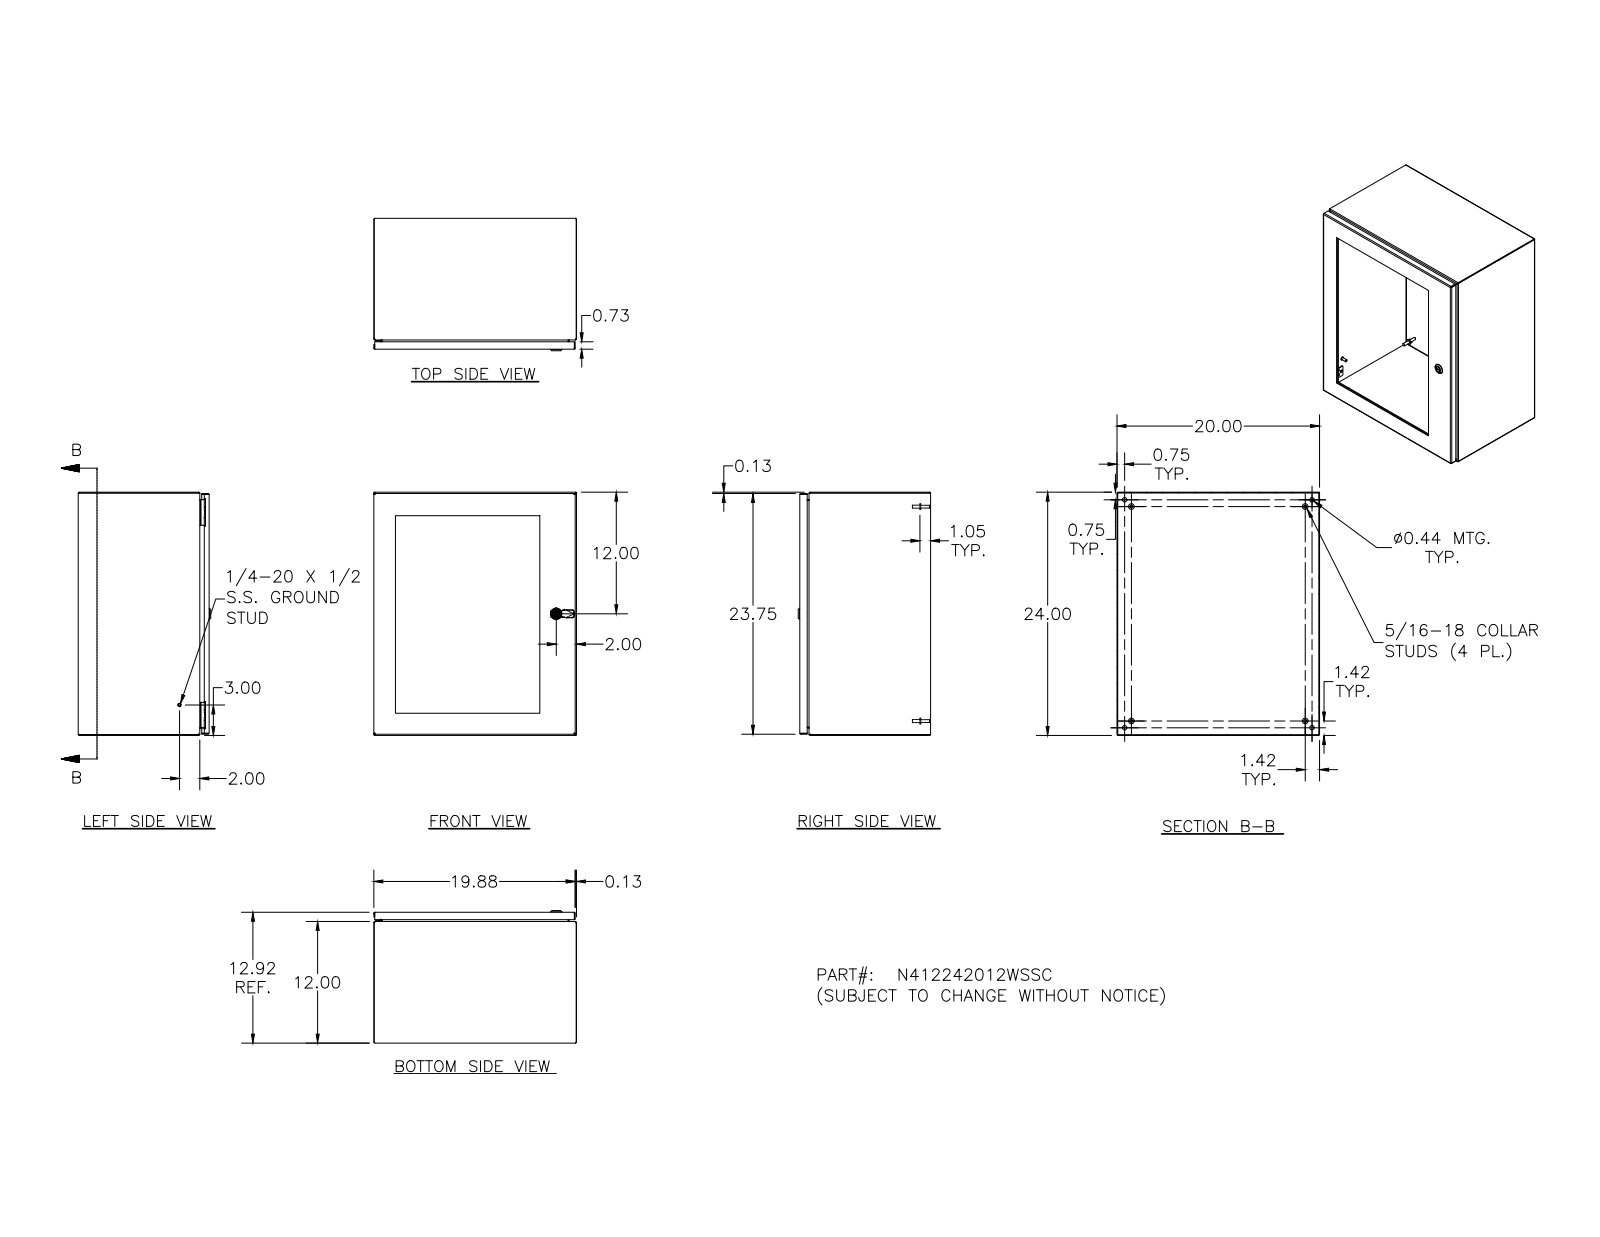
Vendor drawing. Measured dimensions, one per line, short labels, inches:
name: N412242012WSSC; N412242012WSSCBKP; N4122420WSSCLID; HFW328176 (+8 more)
written by: Autodesk Inventor 2011 (AUTOMOTIVE_DESIGN)
unit: in
bodies: 74 solids, 2004 faces (776 planar, 573 cylindrical, 655 other)
size: 24 × 20 × 13.075
volume: 225.8 in³; area: 4 674 in²
holes: 20× ⌀0.156, 18× ⌀0.281, 4× ⌀0.093, 4× ⌀0.152, 4× ⌀0.167, 4× ⌀0.172, 4× ⌀0.188, 4× ⌀0.437, 1× ⌀0.187, 1× ⌀0.197, 1× ⌀0.315, 1× ⌀0.394
bosses: 18× ⌀0.19, 17× ⌀0.253, 10× ⌀0.25, 4× ⌀0.563, 4× ⌀0.36, 4× ⌀0.32, 4× ⌀0.3, 4× ⌀0.275
rounds: 34× R0.031, 26× R0.05, 24× R0.105, 18× R0.016, 16× R0.125, 9× R0.02, 8× R0.032, 4× R0.157
face distances: 0.074, 12.843, 19.926, 12.769, 23.926, 0.25, 12.593, 12.519, 20, 19.852
hole spacings: 4, 8, 16.008, 12, 17.443, 20, 21.132, 15.5
